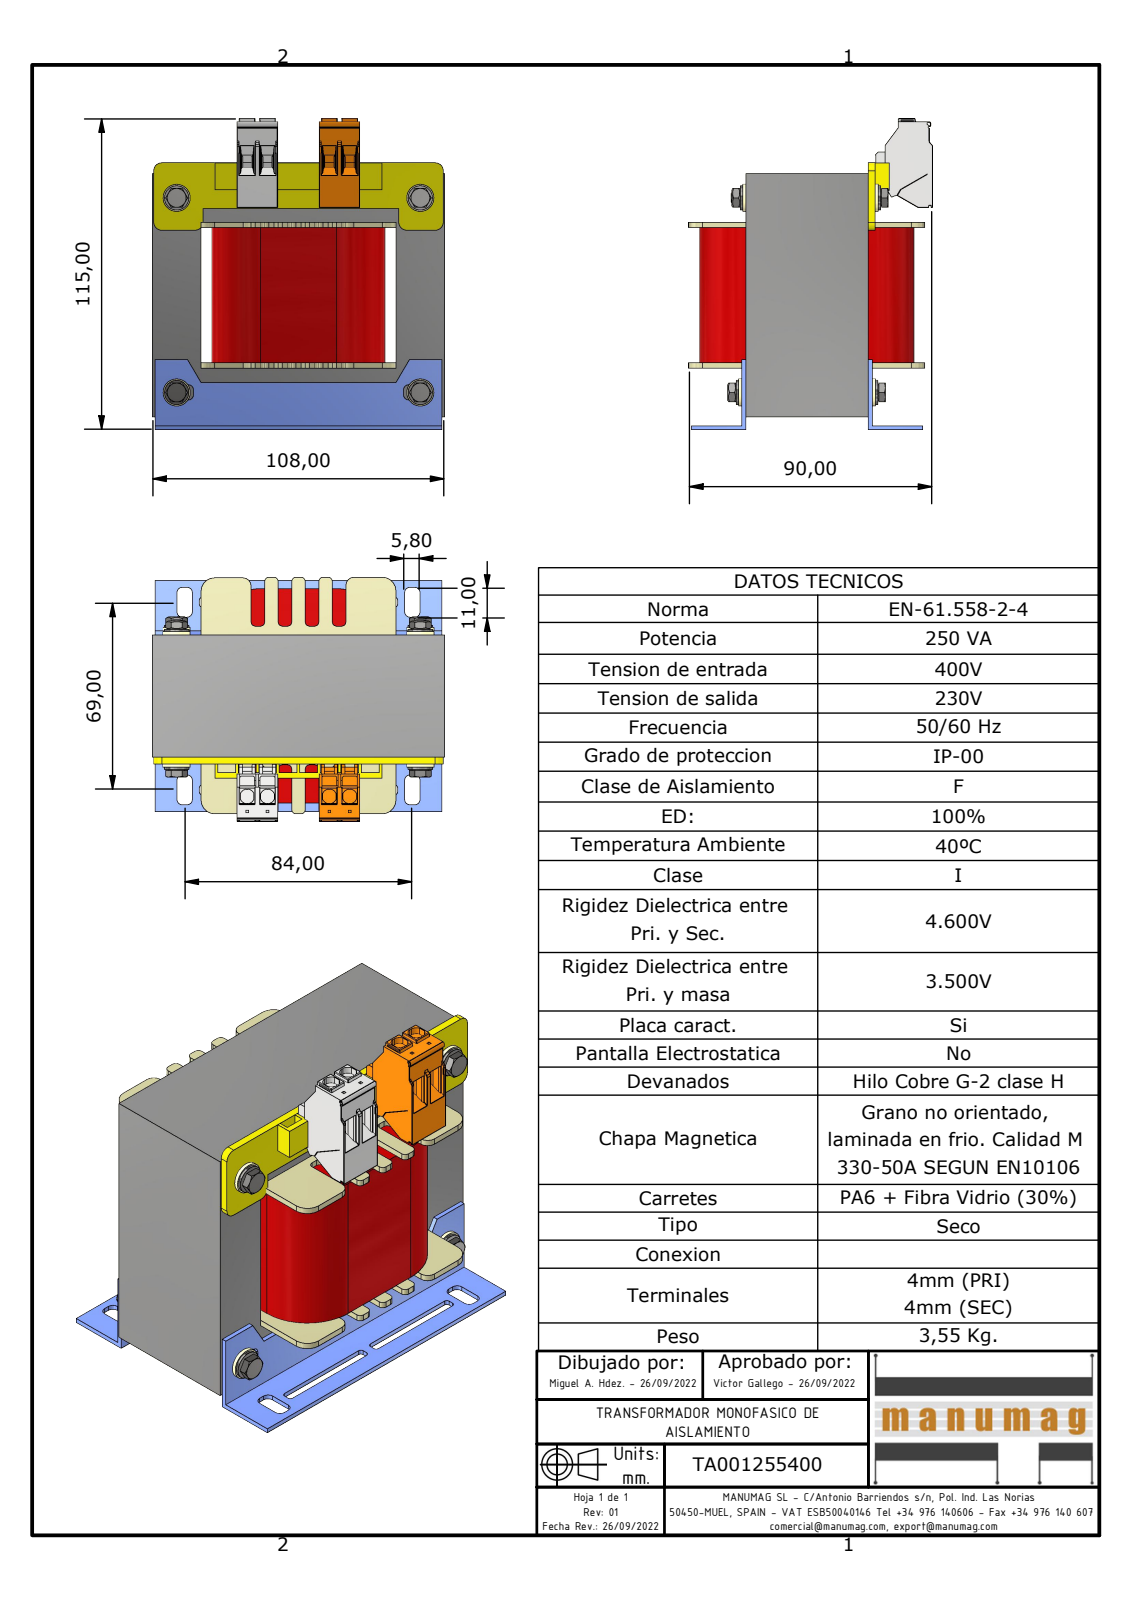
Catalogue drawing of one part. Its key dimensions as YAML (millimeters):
part_name: "TA001255400; EI108 x 90 - 45 (RC36); AF36DIN; EI108 (+7 more)"
step_written_by: "Autodesk Inventor 2023 (AUTOMOTIVE_DESIGN)"
units: millimeters
bodies: {solids: 31, faces: 3835, planar: 3043, cylindrical: 550, other: 242}
overall_size: [115.27, 108, 89.9]
volume: 549657
surface_area: 126184
round_holes:
  - {diameter: 3.24, count: 4}
  - {diameter: 4, count: 4}
  - {diameter: 4.3, count: 4}
  - {diameter: 5.6, count: 4}
round_bosses_or_shafts:
  - {diameter: 10, count: 4}
  - {diameter: 9, count: 4}
  - {diameter: 5.9, count: 4}
  - {diameter: 4.9, count: 4}
  - {diameter: 3.62, count: 4}
partial_cylinders:
  - {radius: 0.15, count: 160}
  - {radius: 0.2, count: 48}
  - {radius: 1.5, count: 28}
  - {radius: 2, count: 24}
  - {radius: 1, count: 20}
  - {radius: 0.5, count: 12}
  - {radius: 3, count: 10}
  - {radius: 5, count: 8}
face_to_face_distances: [18, 72, 36, 45, 54, 90, 1.5, 50, 4, 2]
hole_center_spacings: [72, 90, 115.26]
